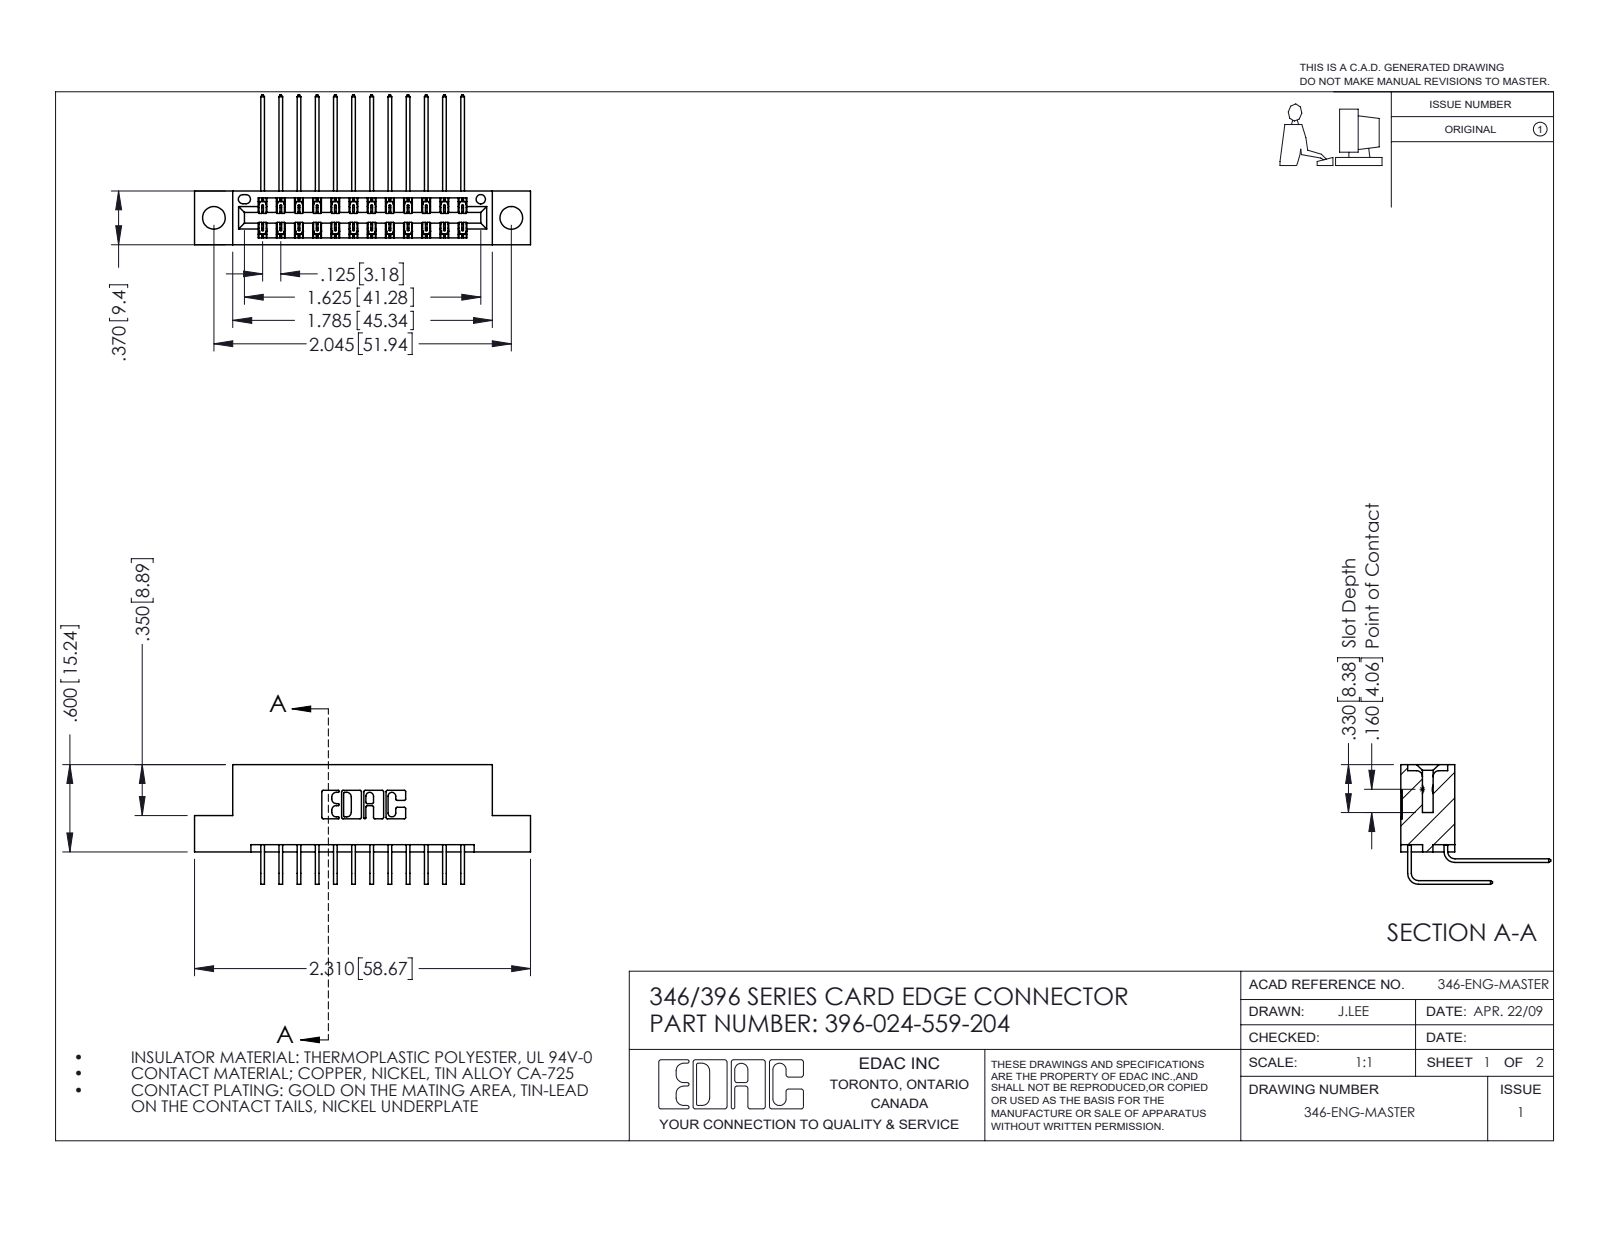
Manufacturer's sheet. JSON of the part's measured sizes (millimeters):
{"part_name": "345-292-001_559 Tail - 2; 396-024-559-204; 345-292-001_558 559 Tail - 1; 346 Part_Flush Mounting Lugs - 0.156 Dia-TH", "step_written_by": "SolidWorks 2016 (CONFIG_CONTROL_DESIGN)", "units": "millimeters", "bodies": {"solids": 25, "faces": 1418, "planar": 964, "cylindrical": 454, "other": 0}, "overall_size": [58.7, 26.2, 20.9], "volume_mm3": 5540, "surface_area_mm2": 7619, "round_holes": [[4, 2], [1.6, 1]], "partial_cylinders_radius": [[0.2, 36], [0.3, 22], [0.2, 6], [0.8, 6], [0.7, 3], [0.4, 2], [0.6, 2], [0.6, 2]], "face_to_face_distances": [1.2, 8.2, 6.4, 9.4, 0.6, 1.8, 7.6, 7, 3.8, 5.6], "hole_center_spacings": [6.2, 46.7, 51.9]}
